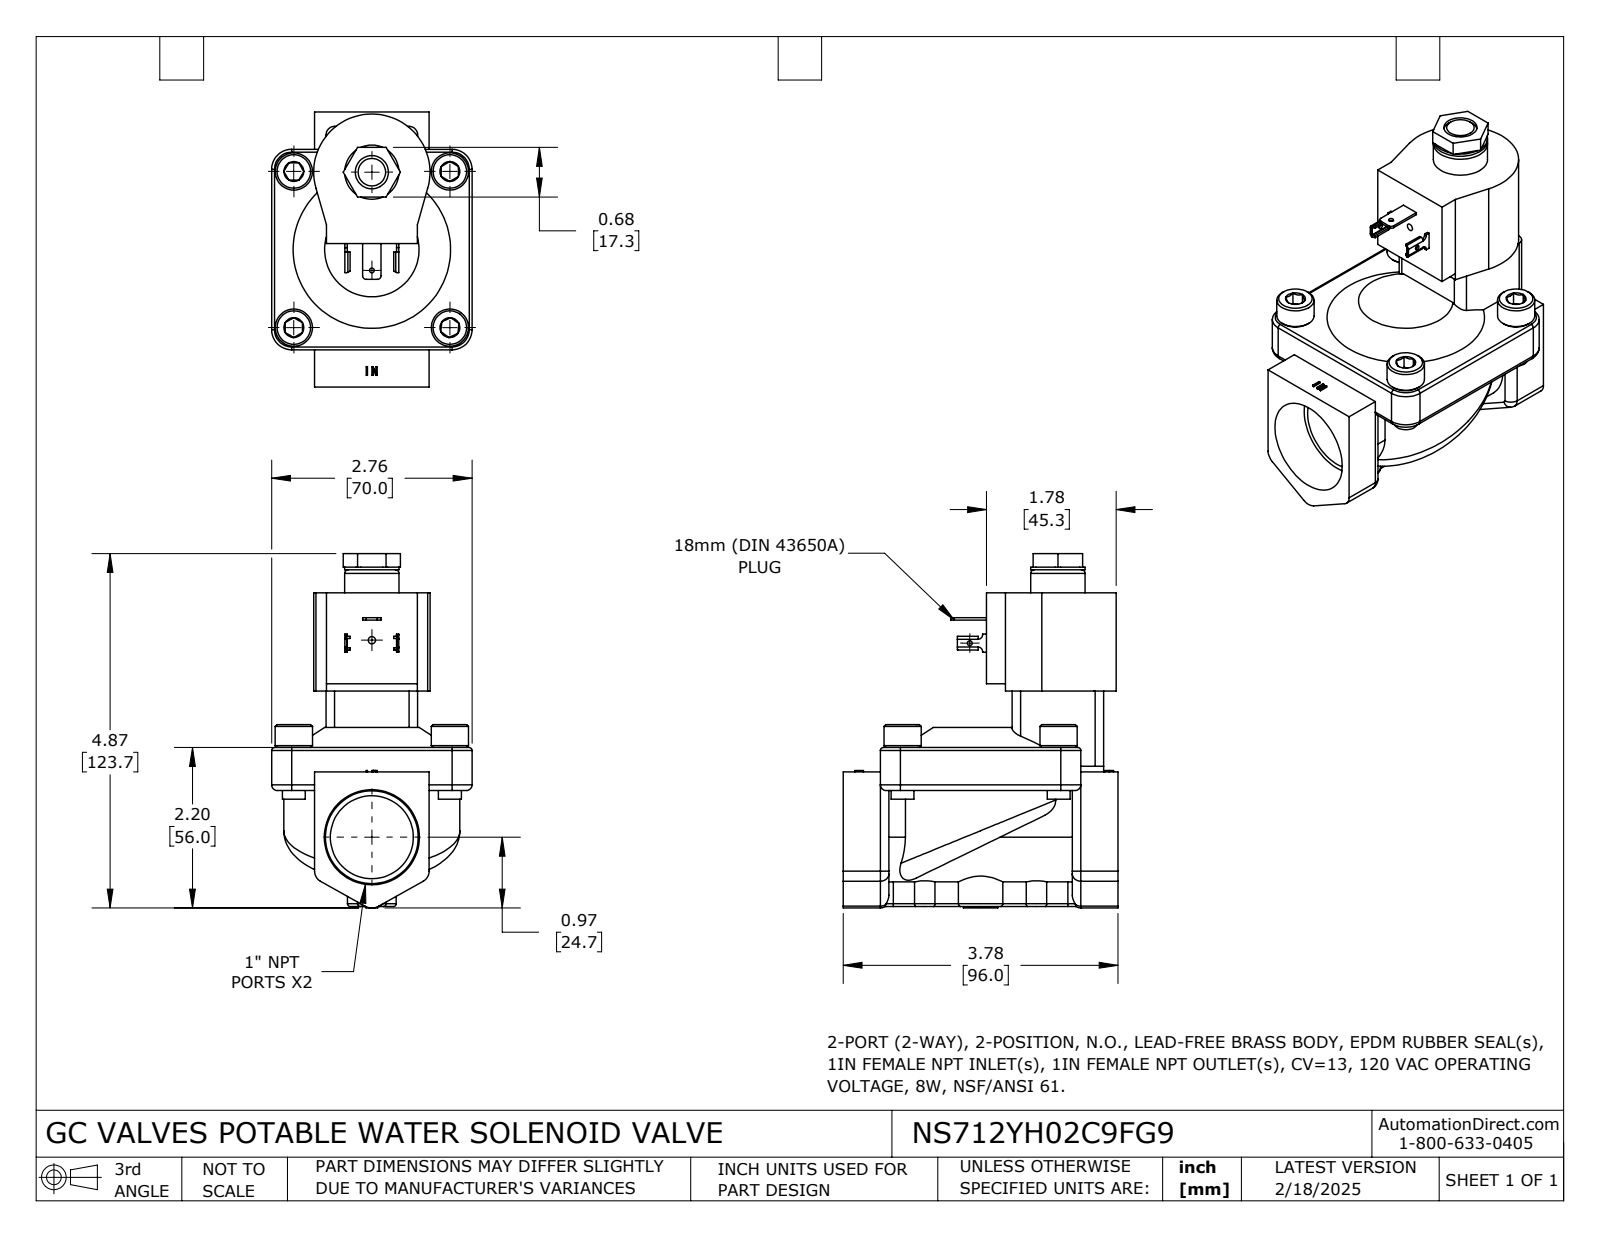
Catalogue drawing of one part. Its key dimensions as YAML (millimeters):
part_name: "NS712YH02C9FG9"
step_written_by: "SolidWorks 2024 (CONFIG_CONTROL_DESIGN)"
units: millimeters
bodies: {solids: 1, faces: 409, planar: 196, cylindrical: 112, other: 101}
overall_size: [123.71, 96, 70]
volume: 256002
surface_area: 45150
round_holes:
  - {diameter: 1.68, count: 1}
  - {diameter: 1.7, count: 1}
  - {diameter: 2.53, count: 1}
  - {diameter: 11.58, count: 1}
  - {diameter: 28.98, count: 1}
round_bosses_or_shafts:
  - {diameter: 13, count: 4}
  - {diameter: 8, count: 4}
  - {diameter: 18.95, count: 1}
partial_cylinders:
  - {radius: 3, count: 12}
  - {radius: 1, count: 6}
  - {radius: 0.15, count: 4}
  - {radius: 1.04, count: 4}
  - {radius: 2, count: 4}
  - {radius: 7, count: 4}
  - {radius: 5, count: 3}
  - {radius: 1.27, count: 2}
face_to_face_distances: [15, 4, 36, 53.99, 19, 51, 55, 32, 7, 6.5]
hole_center_spacings: [34.29, 68.76]
